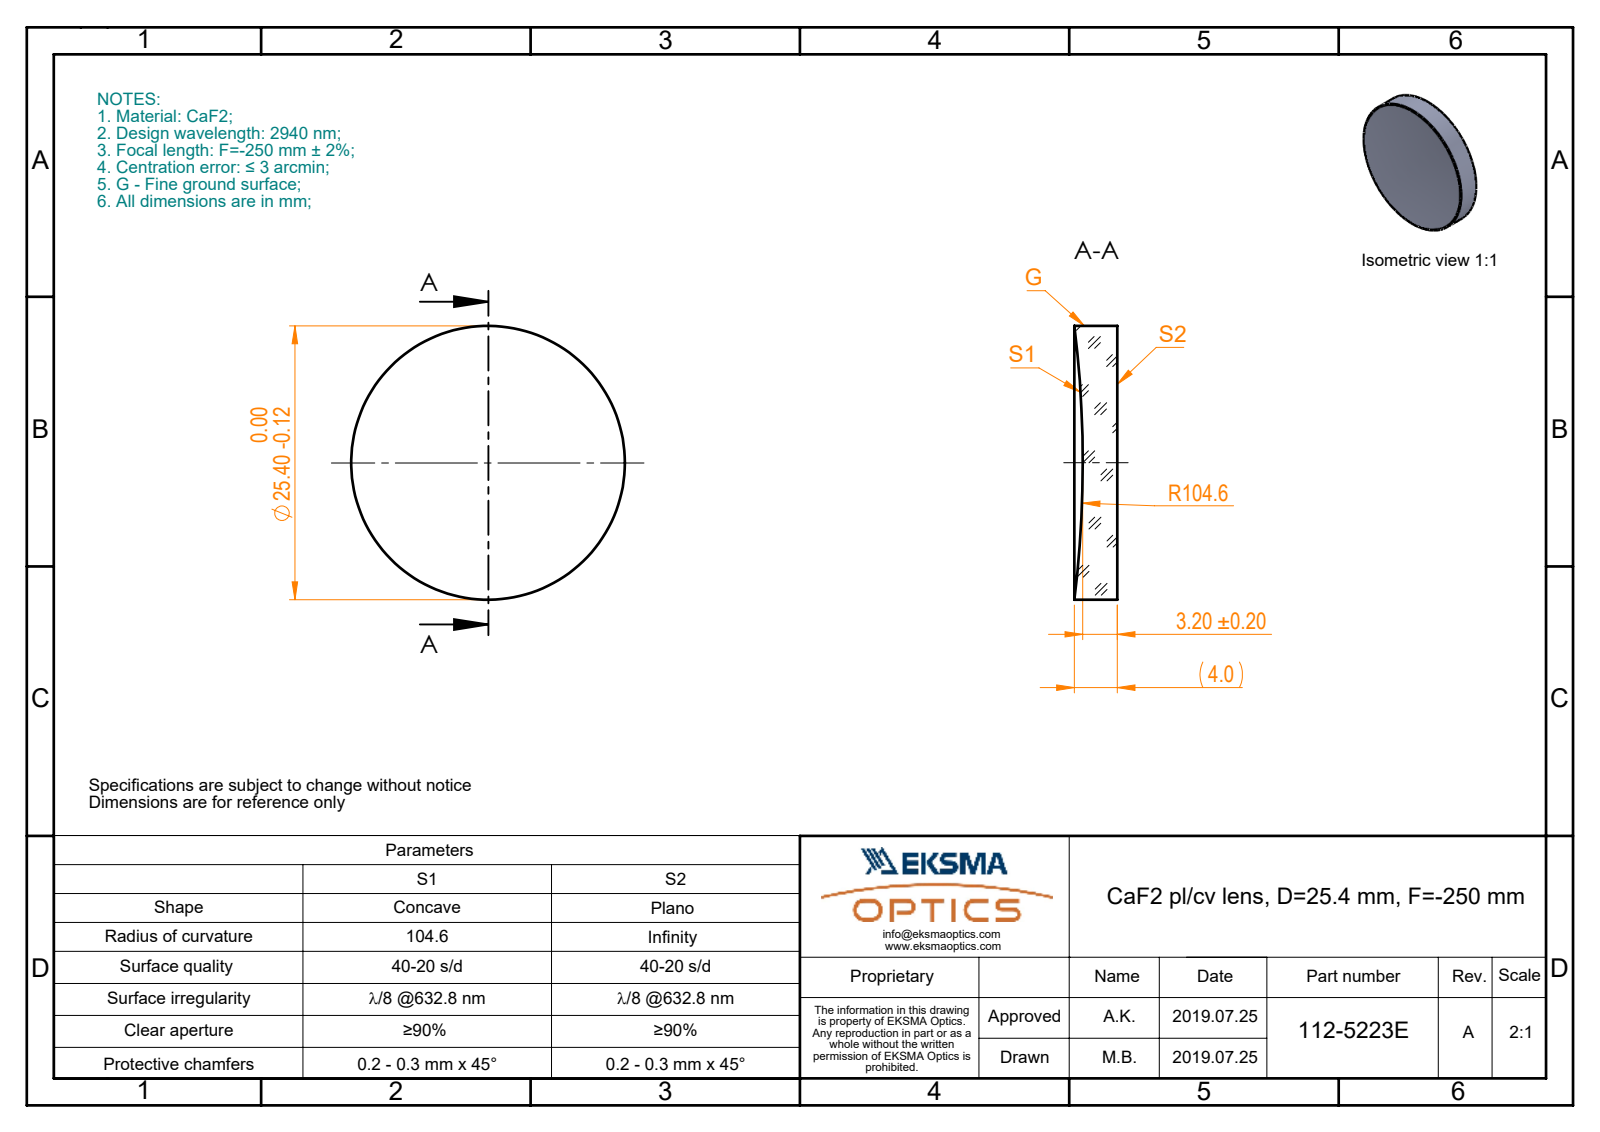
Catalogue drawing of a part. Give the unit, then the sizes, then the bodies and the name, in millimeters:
Units: millimetres
Overall size (bounding box): 25.4 × 25.4 × 3.97
Round bosses / shafts (diameter × count): ⌀25.4 ×1
Volume: 1 817 mm³ · Surface area: 1 332 mm²
Bodies: 1 solid, 5 faces (1 planar, 2 cylindrical, 2 other)
Part name (STEP PRODUCT): 112-5223E CaF2 pl-cv 12.7 F-250
STEP written by: SolidWorks 2017 (CONFIG_CONTROL_DESIGN)
